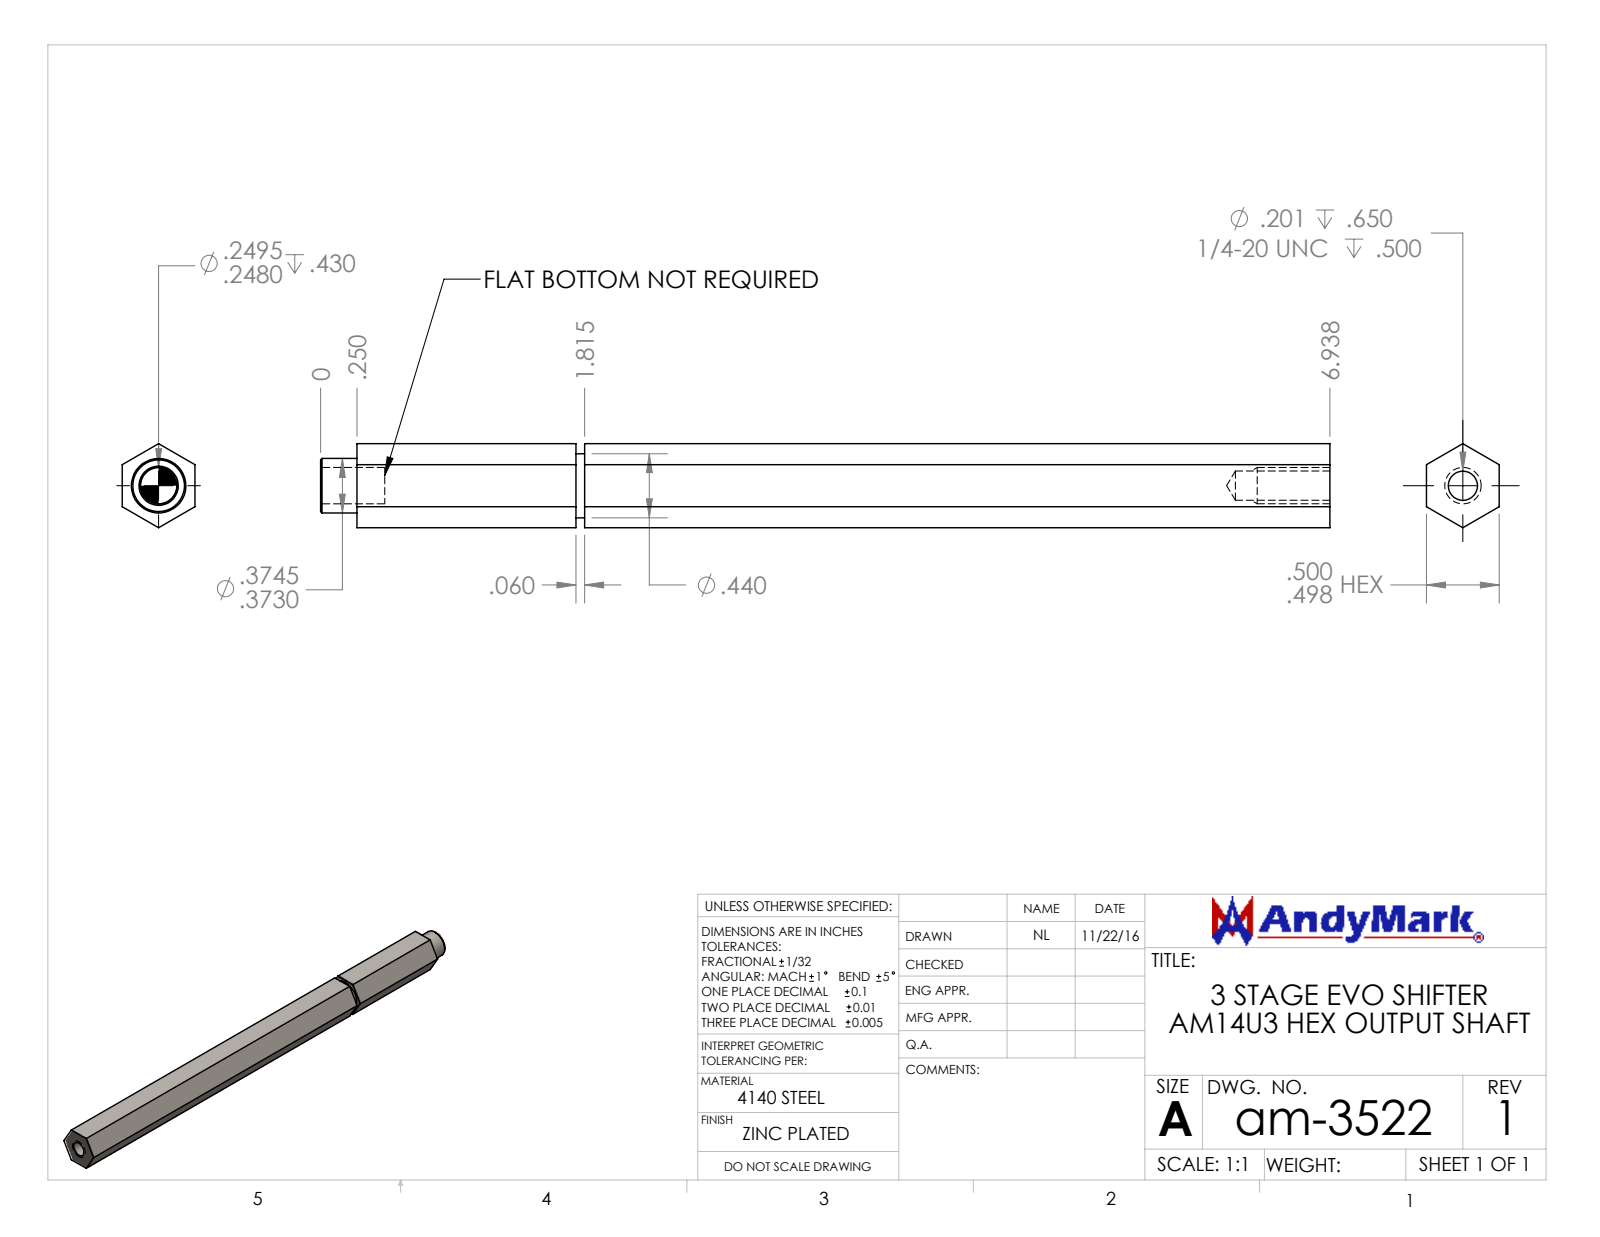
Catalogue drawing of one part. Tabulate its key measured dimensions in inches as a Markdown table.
| quantity | value |
| --- | --- |
| part name | am-3522 3 Stage Evo Shifter AM14U3 Hex Output Shaft |
| STEP written by | SolidWorks 2017 (AUTOMOTIVE_DESIGN) |
| units | inches |
| bodies | 1 solid, 32 faces (18 planar, 8 cylindrical, 6 other) |
| overall size | 6.938 × 0.577 × 0.5 |
| volume | 1.429 in³ |
| surface area | 13.17 in² |
| round holes (diameter × count) | 0.201 × 1, 0.25 × 1 |
| round bosses / shafts (diameter × count) | 0.44 × 1, 0.375 × 1 |
| main face-to-face distances | 0.5, 6.688, 1.505, 5.183, 1.565, 0.06, 5.123, 0.19, 1.315, 1.375 |
